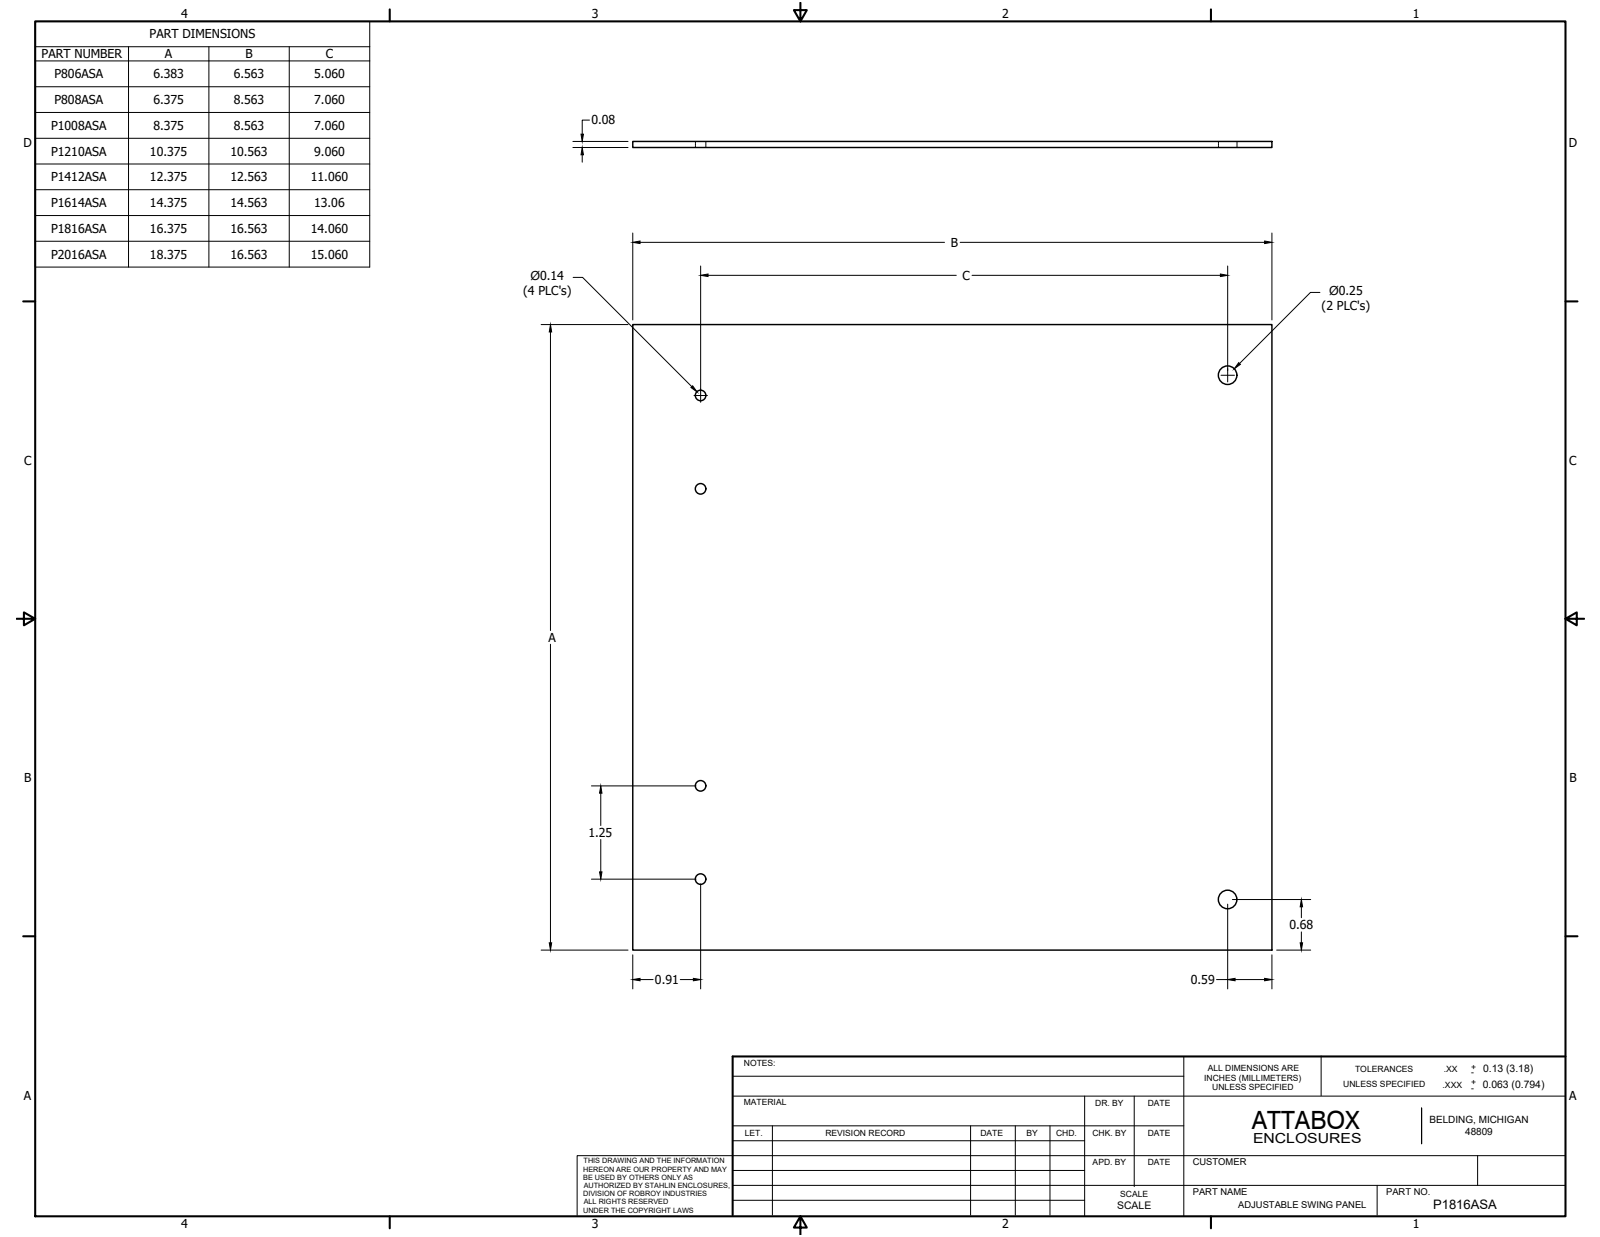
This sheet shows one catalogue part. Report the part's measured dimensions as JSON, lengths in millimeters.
{"part_name": "P1816ASAL", "step_written_by": "Autodesk Inventor 11 (AUTOMOTIVE_DESIGN)", "units": "millimeters", "bodies": {"solids": 1, "faces": 12, "planar": 6, "cylindrical": 6, "other": 0}, "overall_size": [420.7, 415.9, 2], "volume_mm3": 355300, "surface_area_mm2": 353300, "round_holes": [[3.6, 4], [6.4, 2]], "face_to_face_distances": [2, 415.9, 420.7], "hole_center_spacings": [31.8, 335.9, 382.6, 384.5, 513.7, 535.4, 304.2, 367.7]}
